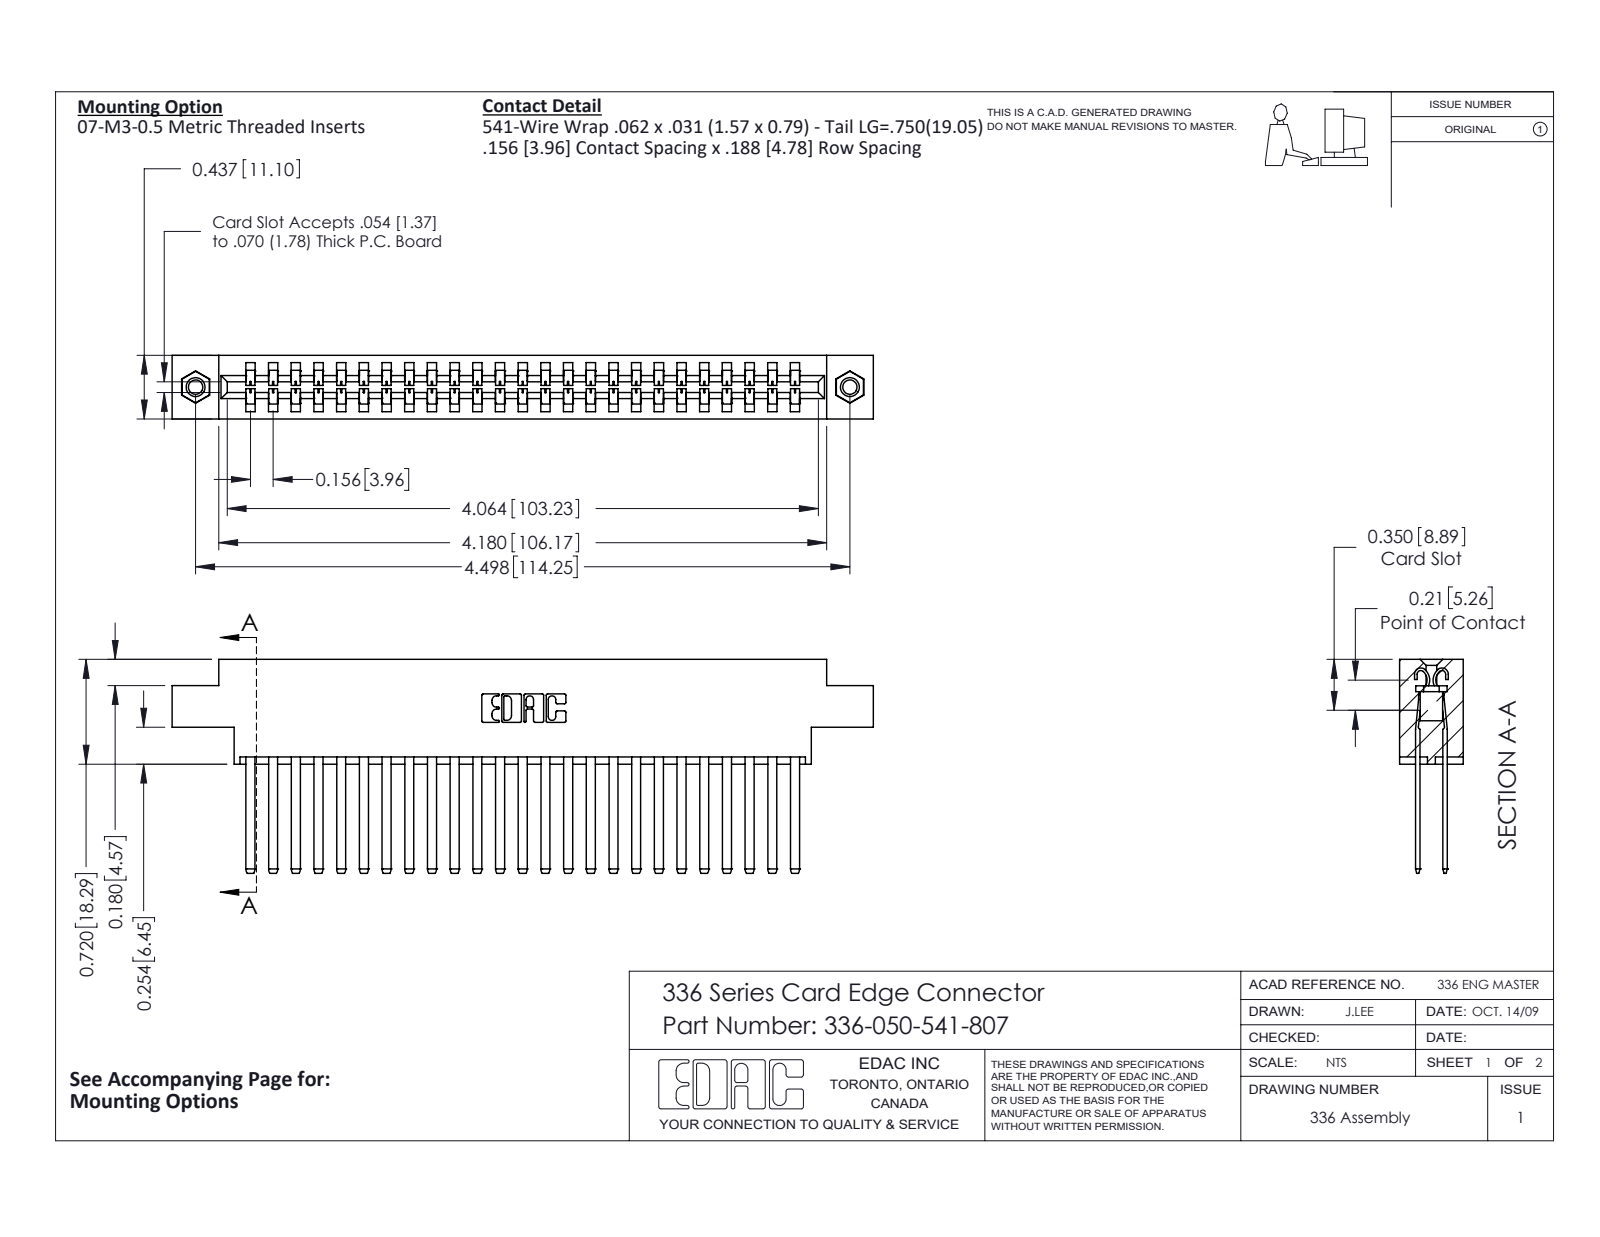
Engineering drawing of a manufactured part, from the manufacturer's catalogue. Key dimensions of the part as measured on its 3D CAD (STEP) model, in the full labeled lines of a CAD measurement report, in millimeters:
Part name (STEP PRODUCT): 336 Part_Offset - .156 Dia - TI; 336-290-001_336-290-541; 345-250-001_345-250-005-103; 336-050-541-807
STEP written by: SolidWorks 2020 (CONFIG_CONTROL_DESIGN)
Units: millimetres
Bodies: 53 solids, 2278 faces (1406 planar, 856 cylindrical, 16 other)
Overall size (bounding box): 122.5 × 37.3 × 11.1
Volume: 18 350 mm³ · Surface area: 23 250 mm²
Round holes (diameter × count): ⌀2.5 ×2, ⌀3.2 ×2, ⌀4 ×2
Round bosses / shafts (diameter × count): ⌀3.9 ×2
Partial cylindrical surfaces — rounded edges, fillets, slot ends (radius × count): R0.1 ×100, R1.4 ×50, R0.3 ×22, R0.2 ×6, R0.8 ×6, R0.6 ×4, R1 ×4, R0.7 ×3
Main face-to-face distances: 4.8, 8.3, 3.6, 7.5, 2.8, 0.8, 11.1, 0.8, 4.6, 3.7
Hole centre spacings: 114.2
